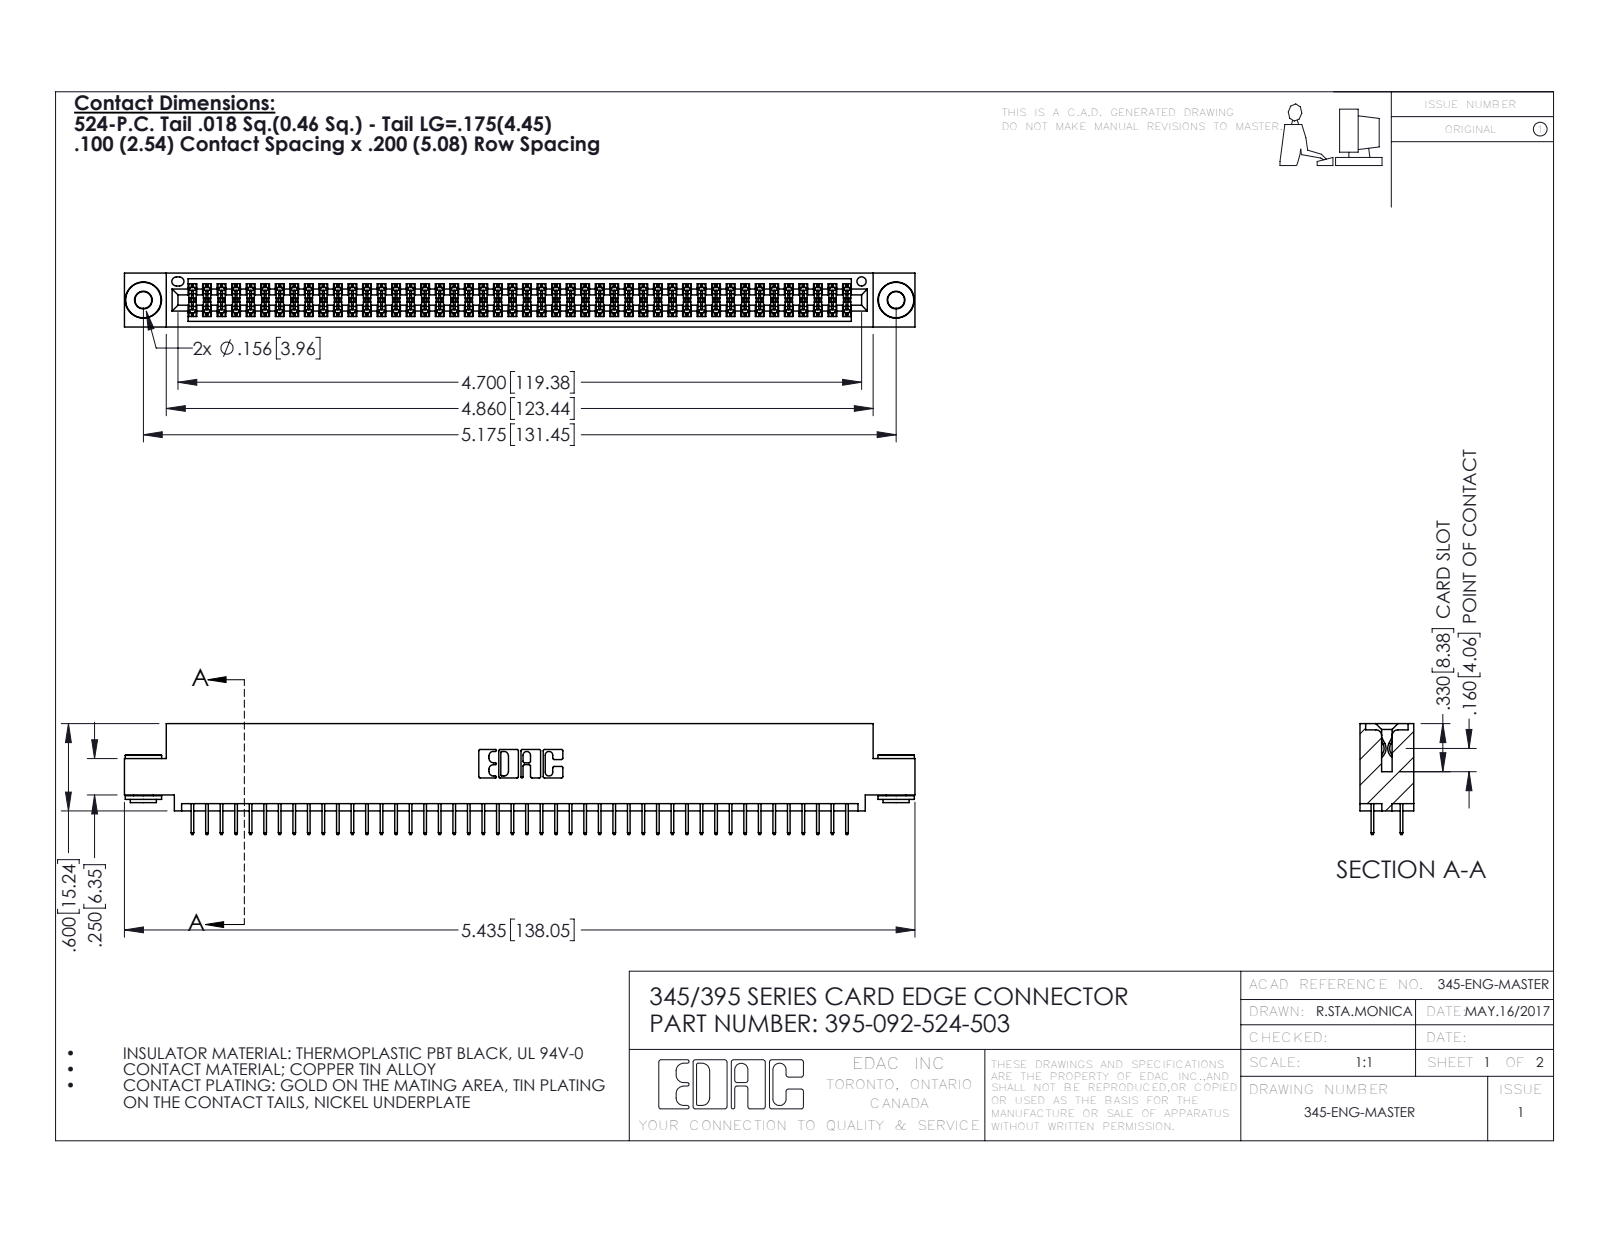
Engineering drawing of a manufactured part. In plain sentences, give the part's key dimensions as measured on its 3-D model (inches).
The part is named "345-292-001_345-293-124; 345 Part_0.110 Offset - 0.156 Dia-TH; 395-092-524-503; 345-250-002_345-250-002-102". Its 3-D file was written by "SolidWorks 2016 (CONFIG_CONTROL_DESIGN)". It is 95 solids with 5136 faces: 3682 planar, 1446 cylindrical and 8 other. Overall it measures 5.435 by 0.762 by 0.37 inches. Its volume is 0.809 cubic inches and its surface area 30.38 square inches. Round holes: 2 of diameter 0.116, 2 of diameter 0.156, 1 of diameter 0.064. Round bosses or shafts: 2 of diameter 0.25, 2 of diameter 0.18, 2 of diameter 0.136. Partial cylindrical surfaces (rounded edges, fillets, slot ends): 138 of radius 0.006, 22 of radius 0.01, 6 of radius 0.007, 6 of radius 0.031, 3 of radius 0.026, 2 of radius 0.014, 2 of radius 0.019, 2 of radius 0.022. The main face-to-face distances are 0.072, 0.298, 0.2, 0.37, 0.025, 0.098, 0.272, 0.225, 0.072, 0.175. The hole center spacings are 0.27, 4.939, 5.175.
